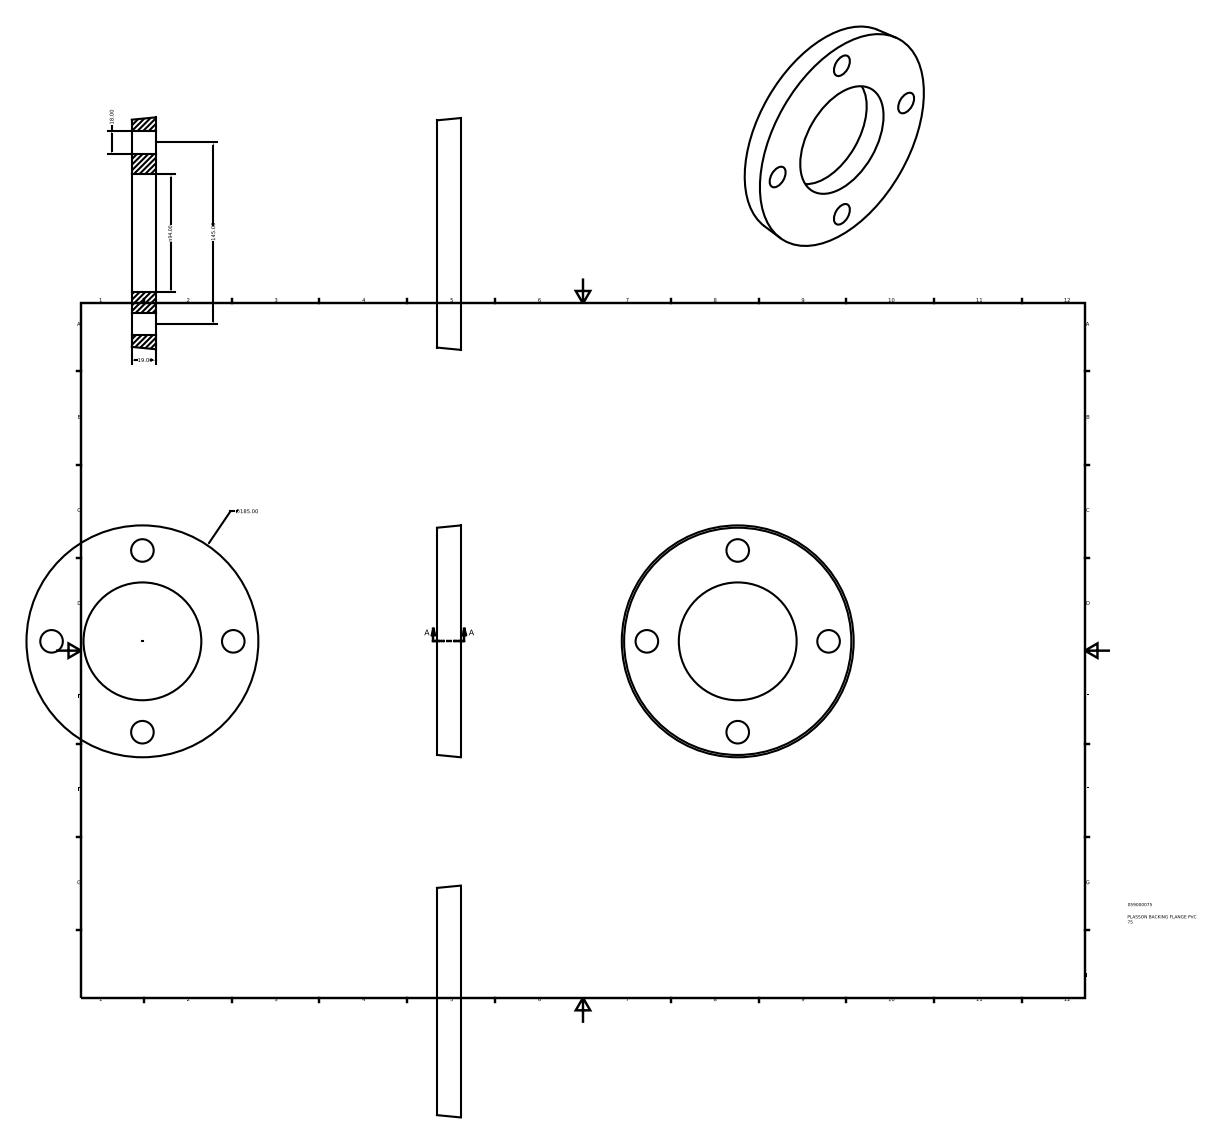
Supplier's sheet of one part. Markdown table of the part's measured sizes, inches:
| quantity | value |
| --- | --- |
| part name | 059000075 |
| STEP written by | Autodesk Inventor 2015 (AUTOMOTIVE_DESIGN) |
| units | inches |
| bodies | 1 solid, 8 faces (2 planar, 5 cylindrical, 1 other) |
| overall size | 7.283 × 7.283 × 0.748 |
| volume | 21.32 in³ |
| surface area | 89.39 in² |
| round holes (diameter × count) | 0.709 × 4, 3.701 × 1 |
| main face-to-face distances | 0.748 |
| hole center spacings | 2.854, 4.037, 5.709 |
